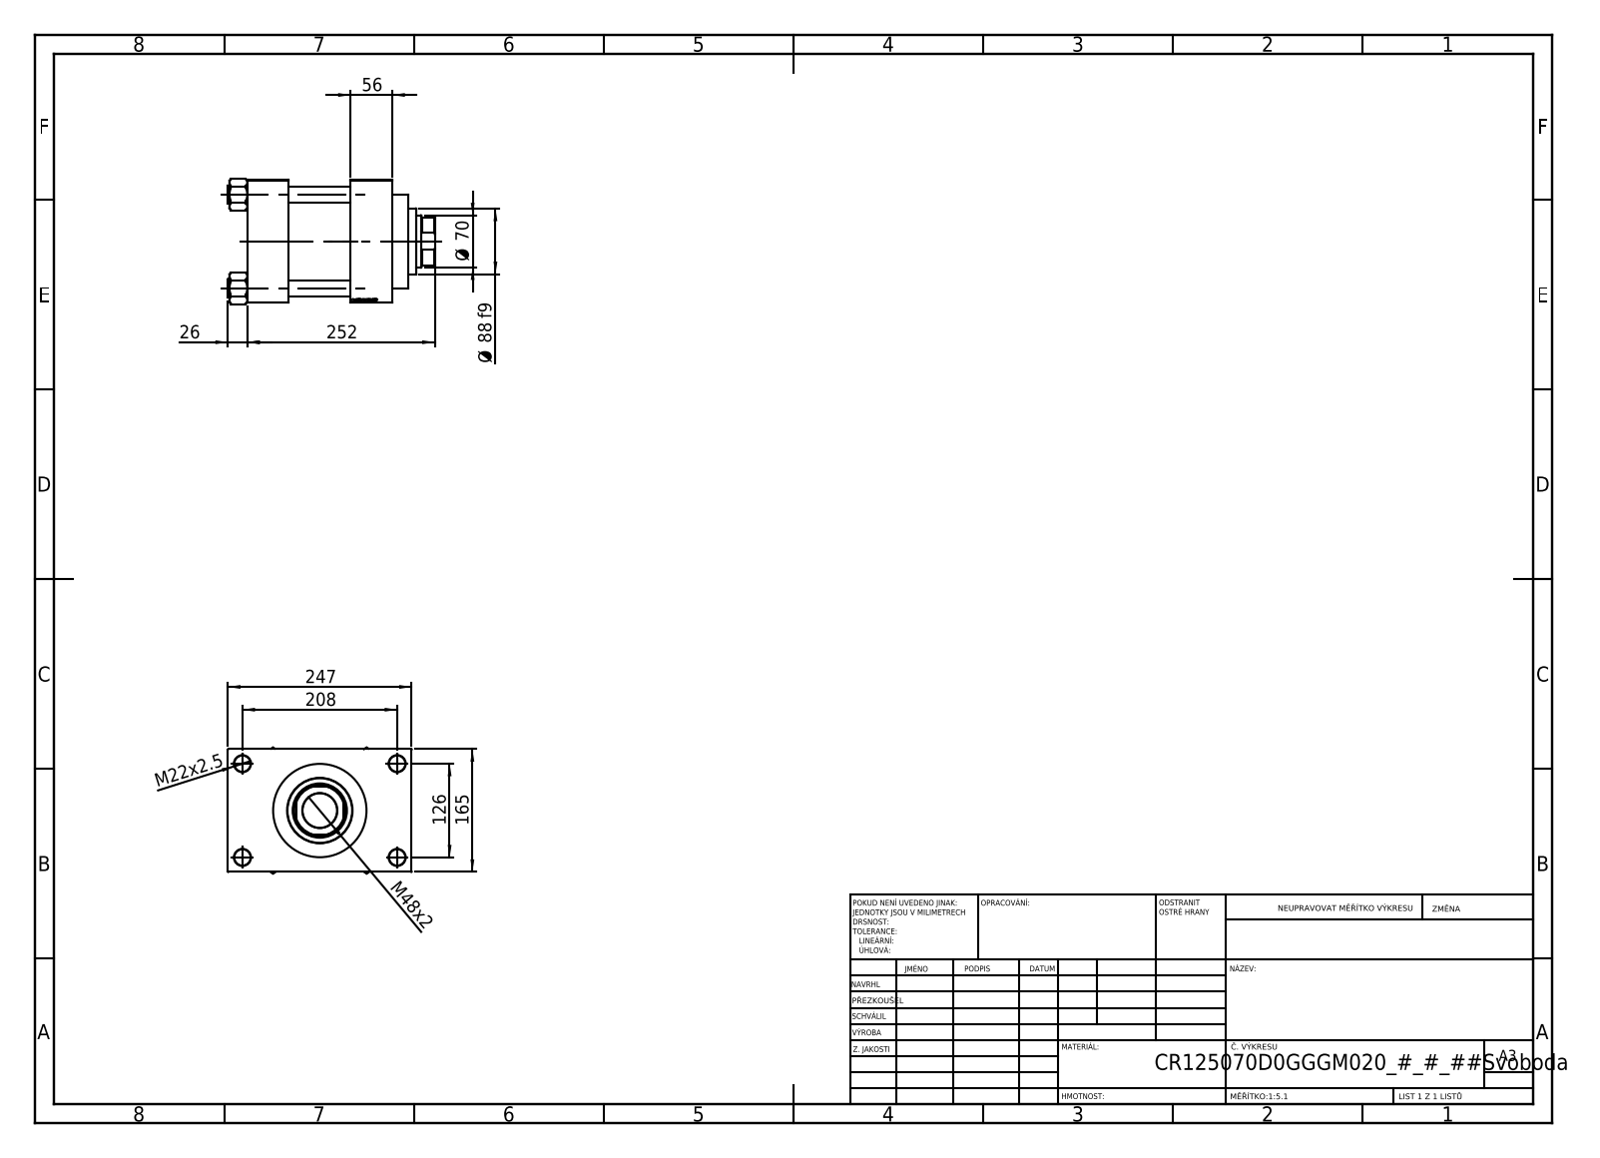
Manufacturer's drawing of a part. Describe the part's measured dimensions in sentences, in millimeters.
The part is named "V215CR_D_Body; V215_VC_A; V215CR_VCP_D; NUT_M5_D (+1 more)". Its 3-D file was written by "SolidWorks 2019 (CONFIG_CONTROL_DESIGN)". It is 11 solids with 1149 faces: 544 planar, 87 cylindrical and 518 other. Overall it measures 278 by 247 by 169.14 millimeters. Its volume is 5 046 000 cubic millimeters and its surface area 538 001 square millimeters. Round holes: 8 of diameter 22, 2 of diameter 7, 2 of diameter 32.24, 2 of diameter 45, 1 of diameter 46.5, 1 of diameter 70, 1 of diameter 73, 1 of diameter 96, 1 of diameter 125, 1 of diameter 125.5. Round bosses or shafts: 4 of diameter 25, 1 of diameter 131, 1 of diameter 88. Partial cylindrical surfaces (rounded edges, fillets, slot ends): 1 of radius 34. The main face-to-face distances are 165, 84, 55, 139, 195, 140, 56, 41, 206, 173.74. The hole center spacings are 41.05, 89.02, 121.59, 125.9, 132.47, 166.95, 209.13, 126.
